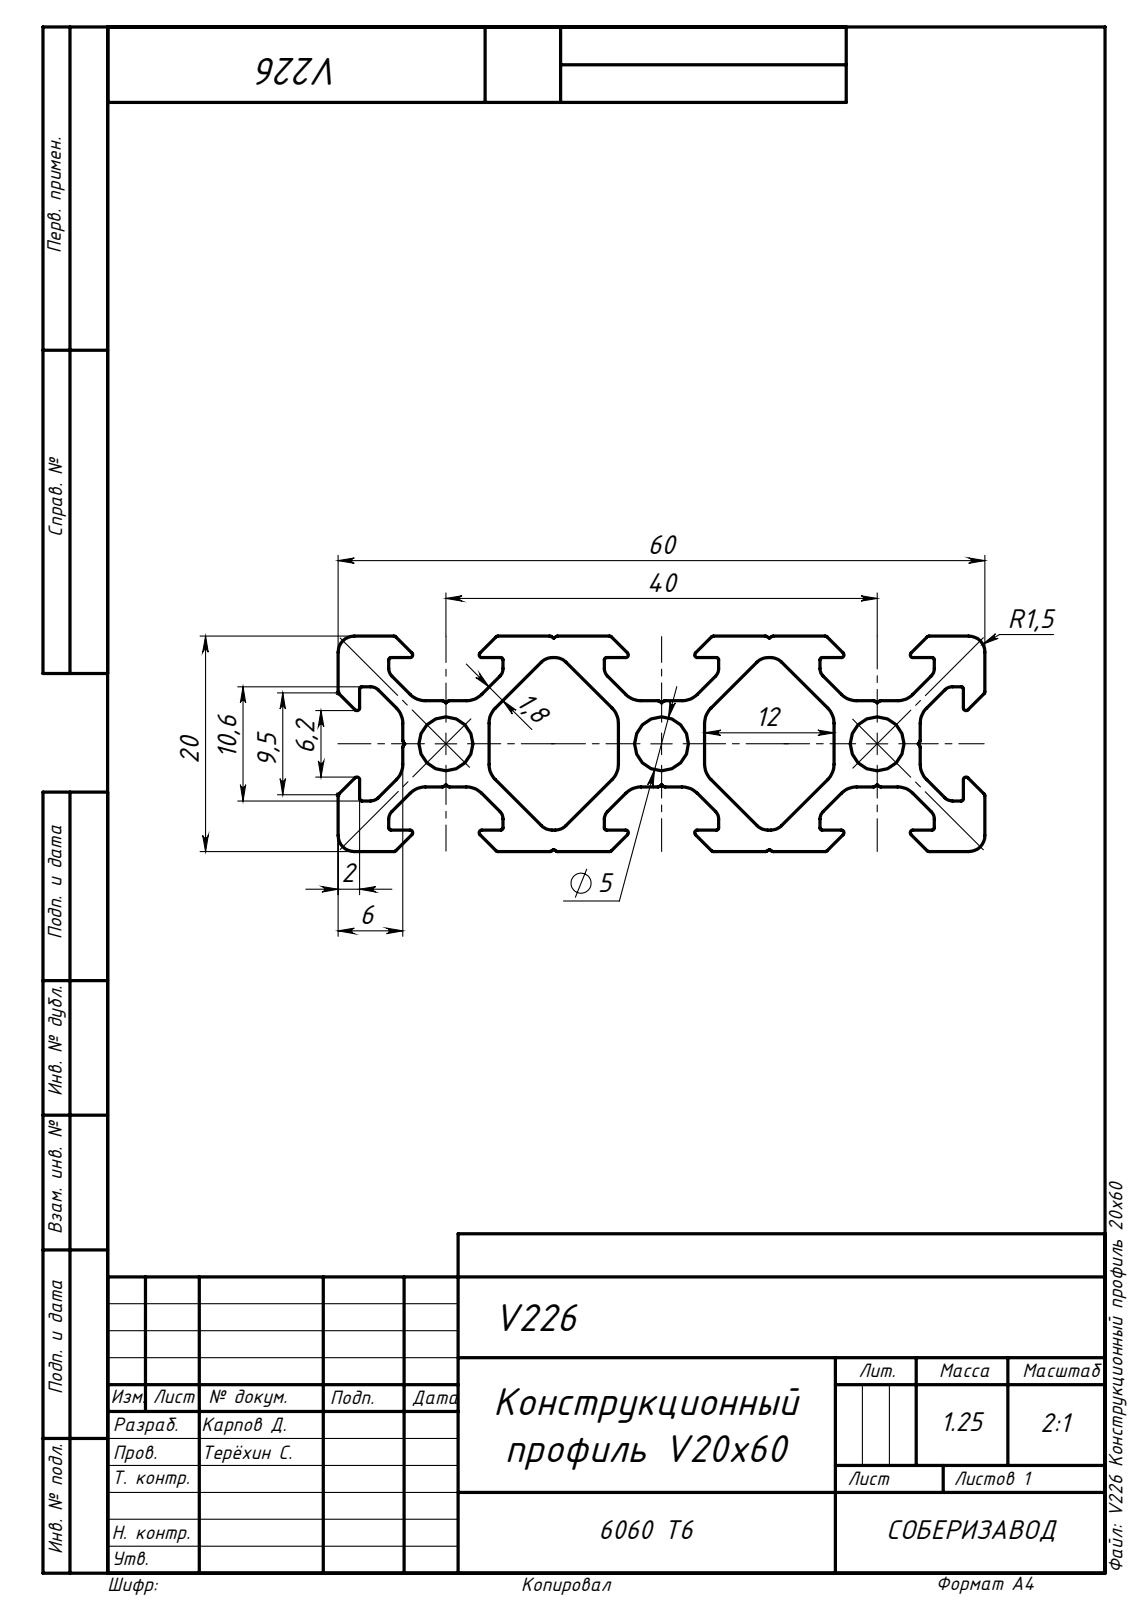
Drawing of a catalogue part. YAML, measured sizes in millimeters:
part_name: "226 Конструкционный профиль 20х60"
step_written_by: "SolidWorks 2014 (AUTOMOTIVE_DESIGN)"
units: millimeters
bodies: {solids: 1, faces: 280, planar: 138, cylindrical: 142, other: 0}
overall_size: [100, 60, 20]
volume: 46185
surface_area: 42336
round_holes:
  - {diameter: 5, count: 3}
partial_cylinders:
  - {radius: 0.25, count: 56}
  - {radius: 2, count: 24}
  - {radius: 0.2, count: 16}
  - {radius: 1, count: 16}
  - {radius: 1.4, count: 8}
  - {radius: 1.5, count: 4}
face_to_face_distances: [14.14, 20, 1.8, 2.83, 4.63, 12.34, 12, 2, 28.28, 14]
hole_center_spacings: [20, 40]
